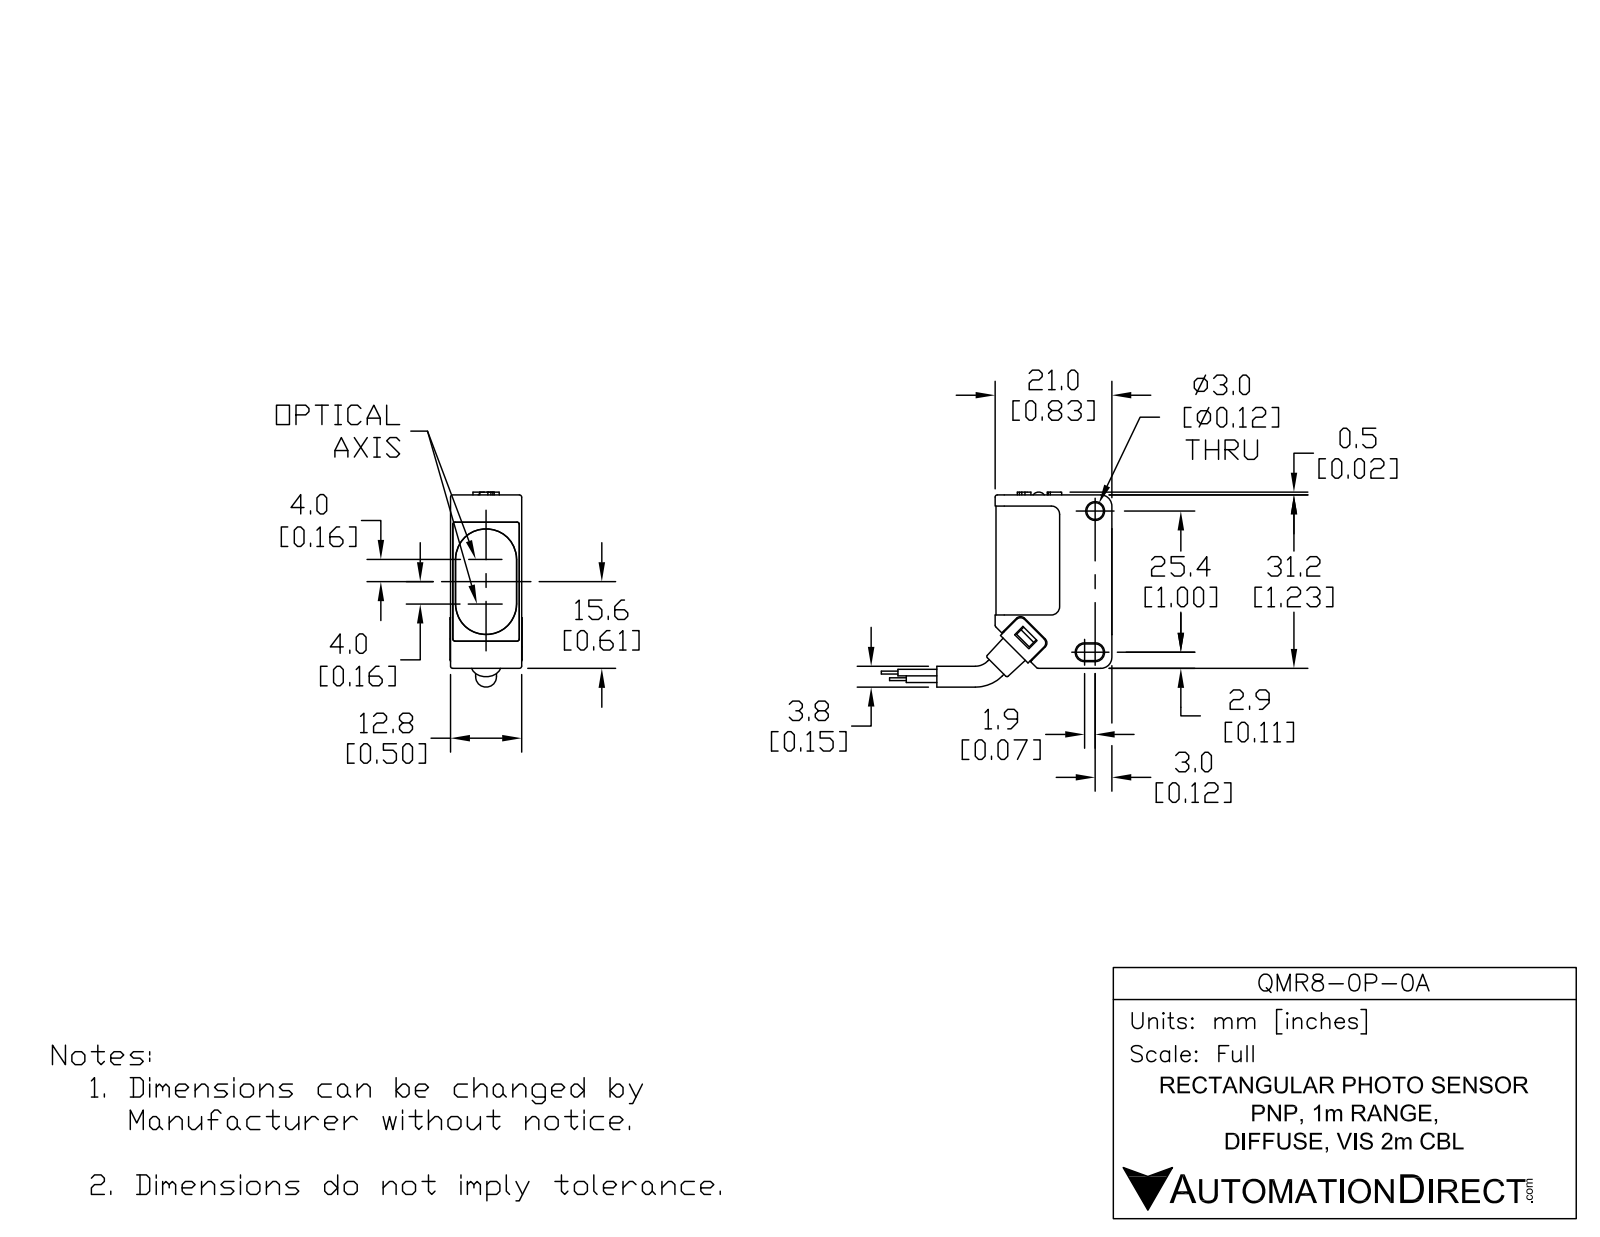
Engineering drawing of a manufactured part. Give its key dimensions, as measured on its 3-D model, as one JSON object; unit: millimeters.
{"part_name": "QMR8-0P-0A", "step_written_by": "SolidWorks 2017 (AUTOMOTIVE_DESIGN)", "units": "millimeters", "bodies": {"solids": 9, "faces": 258, "planar": 134, "cylindrical": 100, "other": 24}, "overall_size": [81.1, 26.2, 13], "volume_mm3": 7700, "surface_area_mm2": 5403, "round_holes": [[3, 3], [3.8, 1], [5.7, 1], [7.2, 1]], "round_bosses_or_shafts": [[3.5, 2]], "partial_cylinders_radius": [[0.4, 13], [0.5, 10], [1, 8], [1.5, 6], [0.6, 4], [0.2, 2], [0.9, 2], [1.1, 2]], "face_to_face_distances": [0.5, 12.6, 1.5, 0.4, 12.8, 3.5, 12.4, 2, 12.2, 12.5], "hole_center_spacings": [5.2]}
